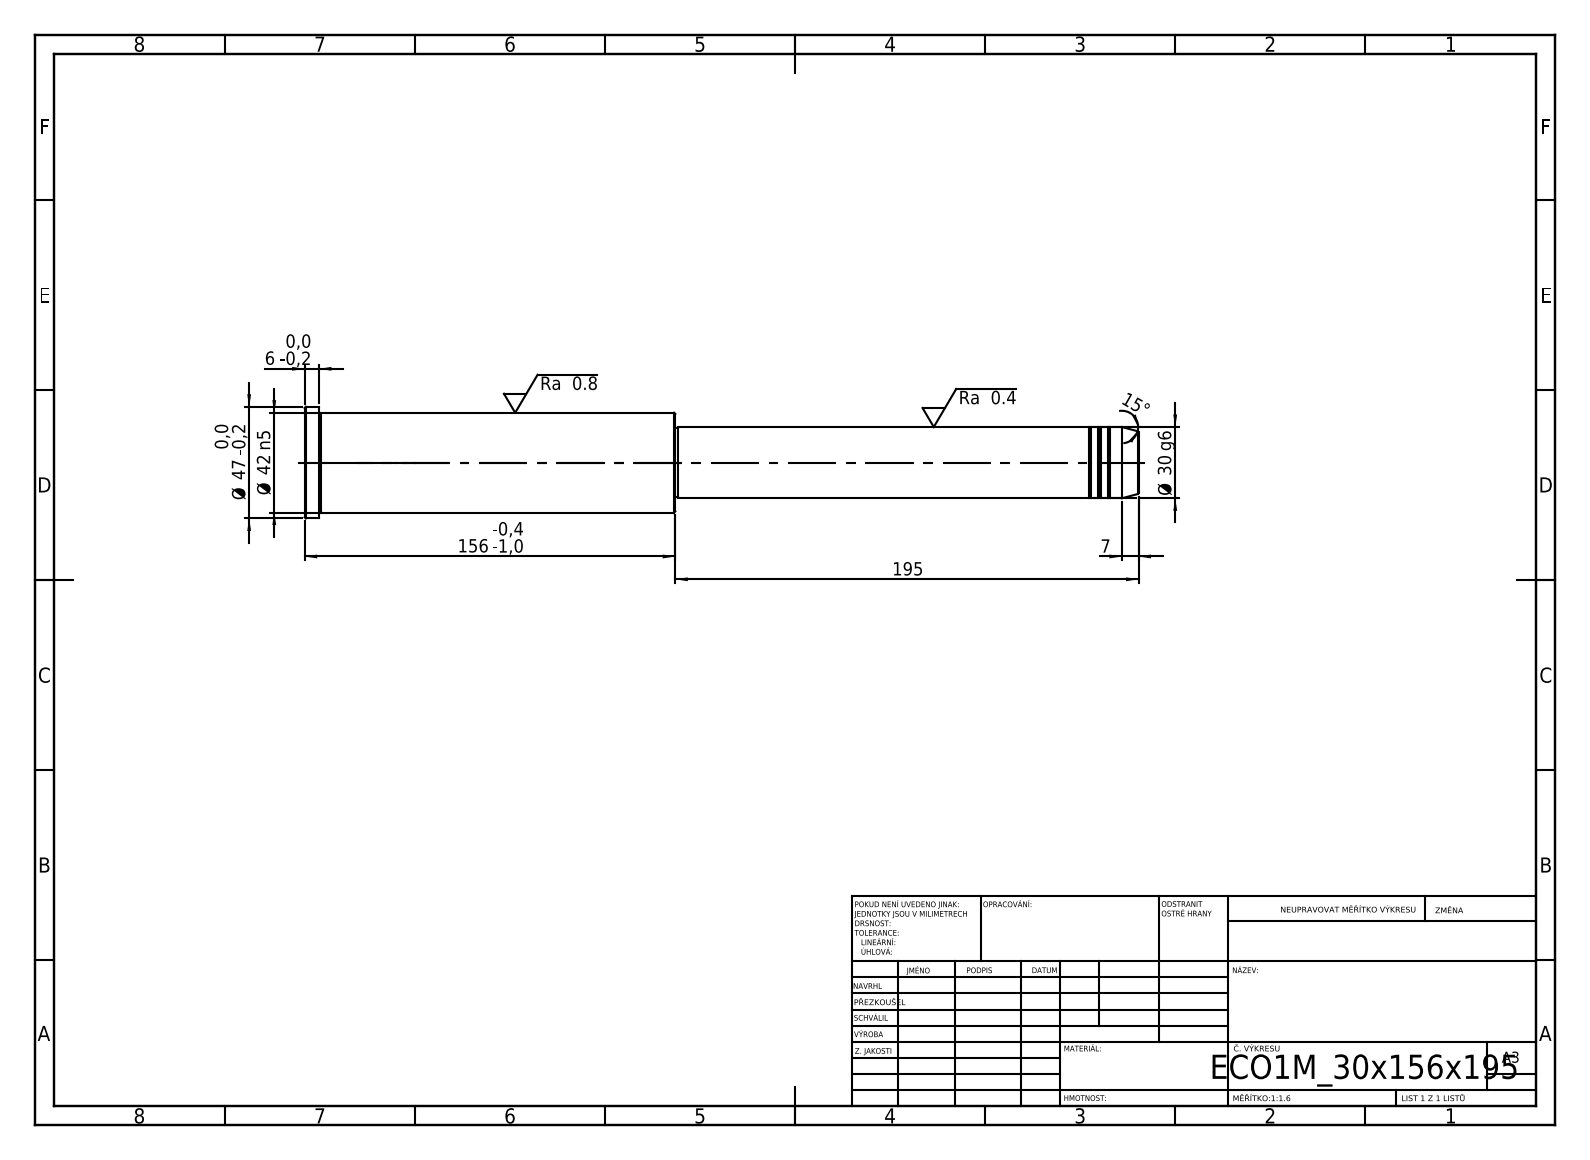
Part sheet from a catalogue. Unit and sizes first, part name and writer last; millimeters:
Units: millimetres
Overall size (bounding box): 351 × 47 × 47
Round bosses / shafts (diameter × count): ⌀47 ×1, ⌀42 ×1, ⌀30 ×1, ⌀29 ×1
Main face-to-face distances: 156, 195, 351, 345, 150, 6, 194, 1, 151, 157
Volume: 355 226 mm³ · Surface area: 42 563 mm²
Bodies: 1 solid, 43 faces (5 planar, 14 cylindrical, 24 other)
STEP written by: SolidWorks 2019 (CONFIG_CONTROL_DESIGN)
